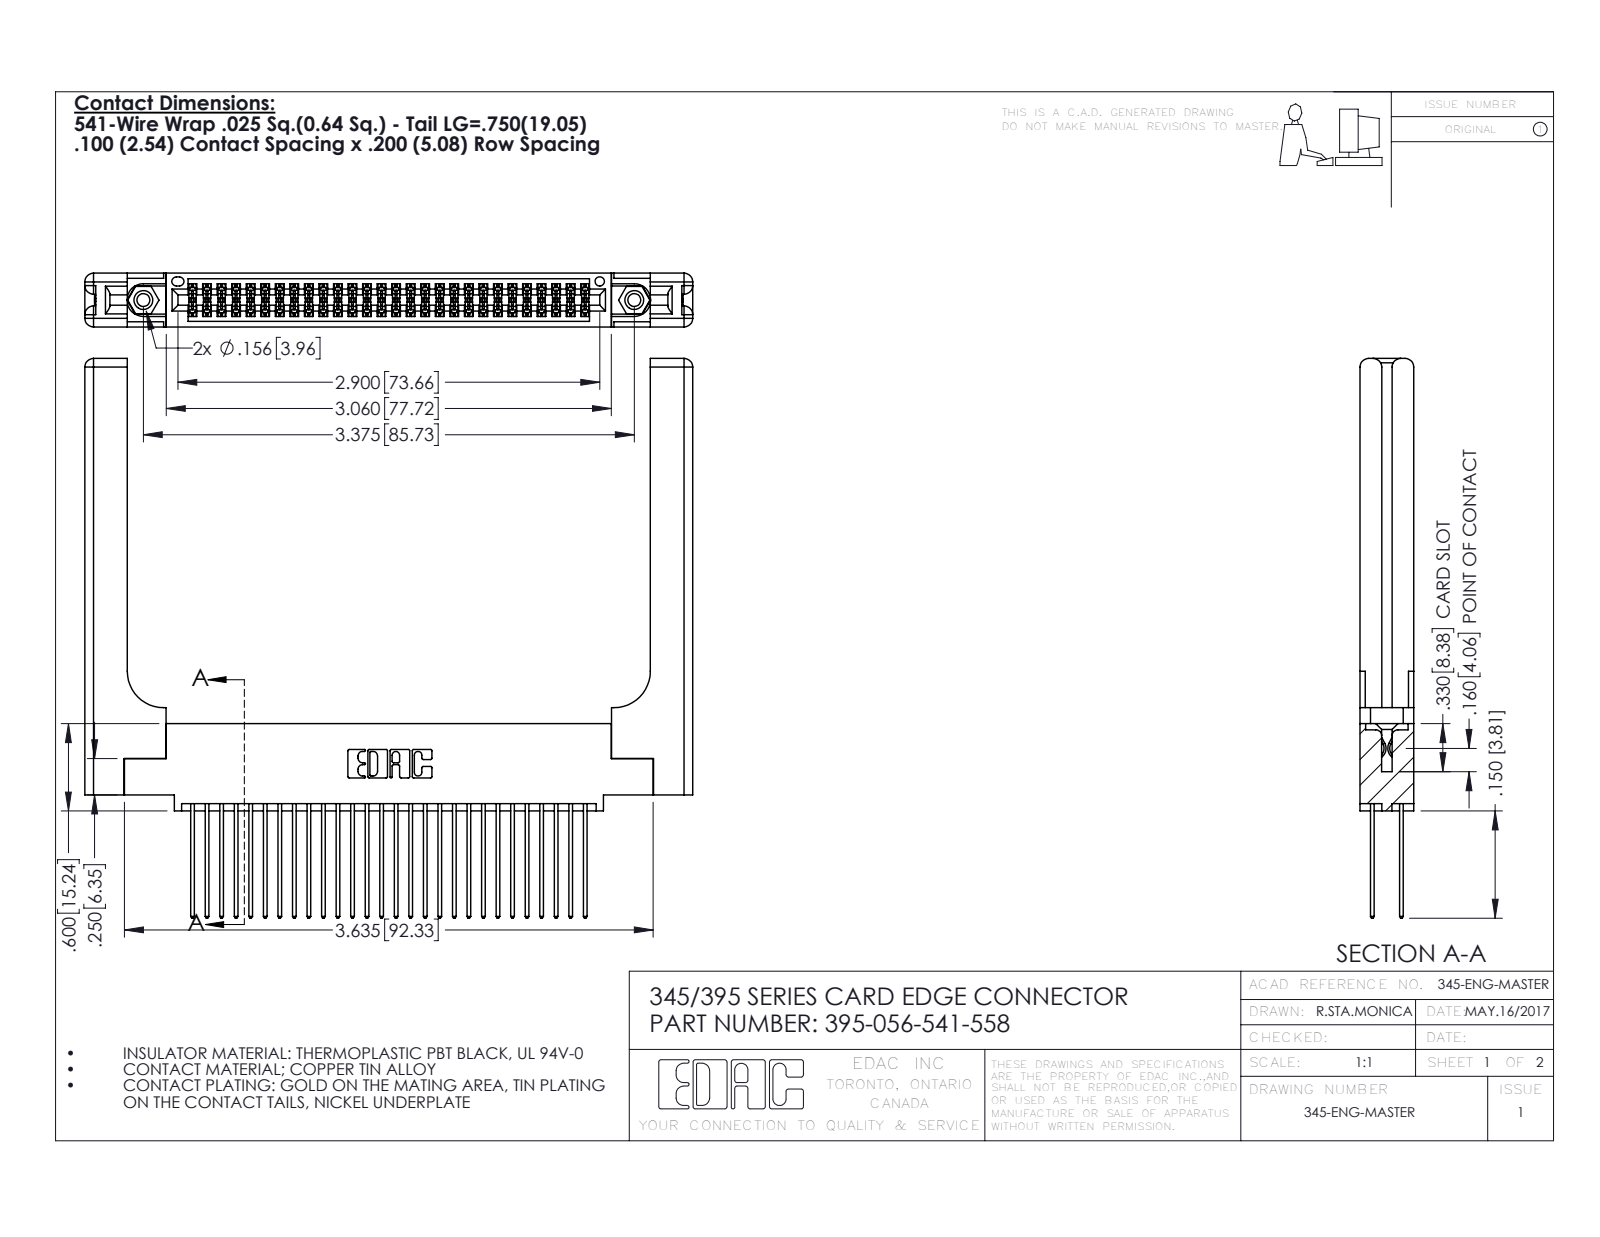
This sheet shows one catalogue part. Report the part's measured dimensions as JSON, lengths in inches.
{"part_name": "345 Part_0.110 Offset - 0.156 Dia-TH; 395-056-541-558; 345-250-001_345-250-001-102; 345-292-001_345-293-141 (+1 more)", "step_written_by": "SolidWorks 2016 (CONFIG_CONTROL_DESIGN)", "units": "inches", "bodies": {"solids": 61, "faces": 3186, "planar": 2080, "cylindrical": 1046, "other": 60}, "overall_size": [4.179, 3.847, 0.37], "volume_in3": 1.154, "surface_area_in2": 33.8, "round_holes": [[0.089, 2], [0.125, 2], [0.156, 2], [0.064, 1]], "round_bosses_or_shafts": [[0.155, 2]], "partial_cylinders_radius": [[0.006, 84], [0.01, 56], [0.01, 22], [0.06, 16], [0.007, 6], [0.031, 6], [0.026, 3], [0.014, 2]], "face_to_face_distances": [0.072, 0.298, 0.37, 0.098, 0.272, 0.025, 0.2, 0.225, 0.148, 0.15], "hole_center_spacings": [0.27, 3.14, 3.375]}
